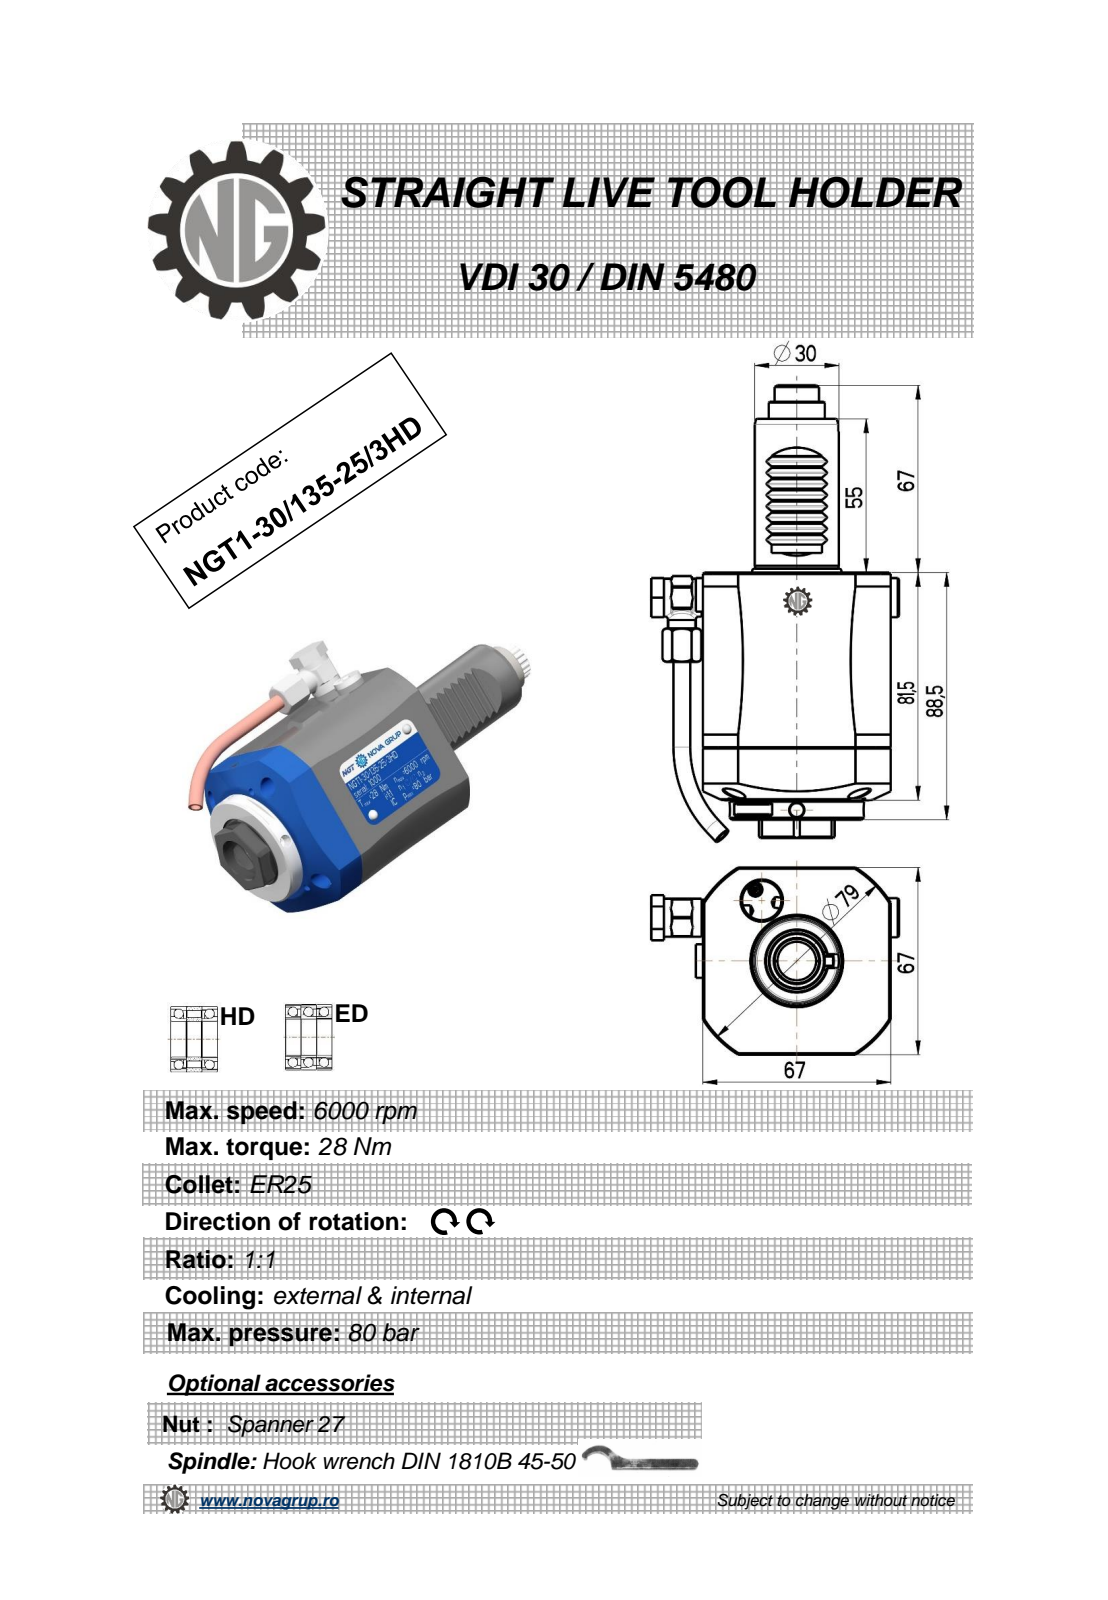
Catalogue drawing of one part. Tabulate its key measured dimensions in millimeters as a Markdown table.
| quantity | value |
| --- | --- |
| part name | NGT1_30_135_25_3HD |
| STEP written by | PRO/ENGINEER BY PARAMETRIC TECHNOLOGY CORPORATION, 2010280 (CONFIG_CONTROL_DESIGN) |
| units | millimeters |
| bodies | 2 solids, 450 faces (142 planar, 174 cylindrical, 134 other) |
| overall size | 163.44 × 88.4 × 67 |
| volume | 392 904 mm³ |
| surface area | 42 120 mm² |
| round holes (diameter × count) | 4 × 3, 5 × 2, 3 × 1, 6 × 1, 6.2 × 1, 9 × 1, 10 × 1, 11 × 1, 18 × 1, 26.5 × 1 |
| round bosses / shafts (diameter × count) | 48 × 1, 30 × 1, 20 × 1, 14 × 1, 13.6 × 1, 13 × 1, 12 × 1, 10 × 1 |
| partial cylindrical surfaces (radius × count) | 1.98 × 36, 0.3 × 8, 0.41 × 6, 0.5 × 4, 7.08 × 1, 7.7 × 1, 7.92 × 1, 13 × 1 |
| main face-to-face distances | 67, 88.5, 7, 81.5, 12, 2.83, 55, 5.66, 6.5, 150 |
| hole center spacings | 0.4, 43.83, 44.21, 77.56 |
